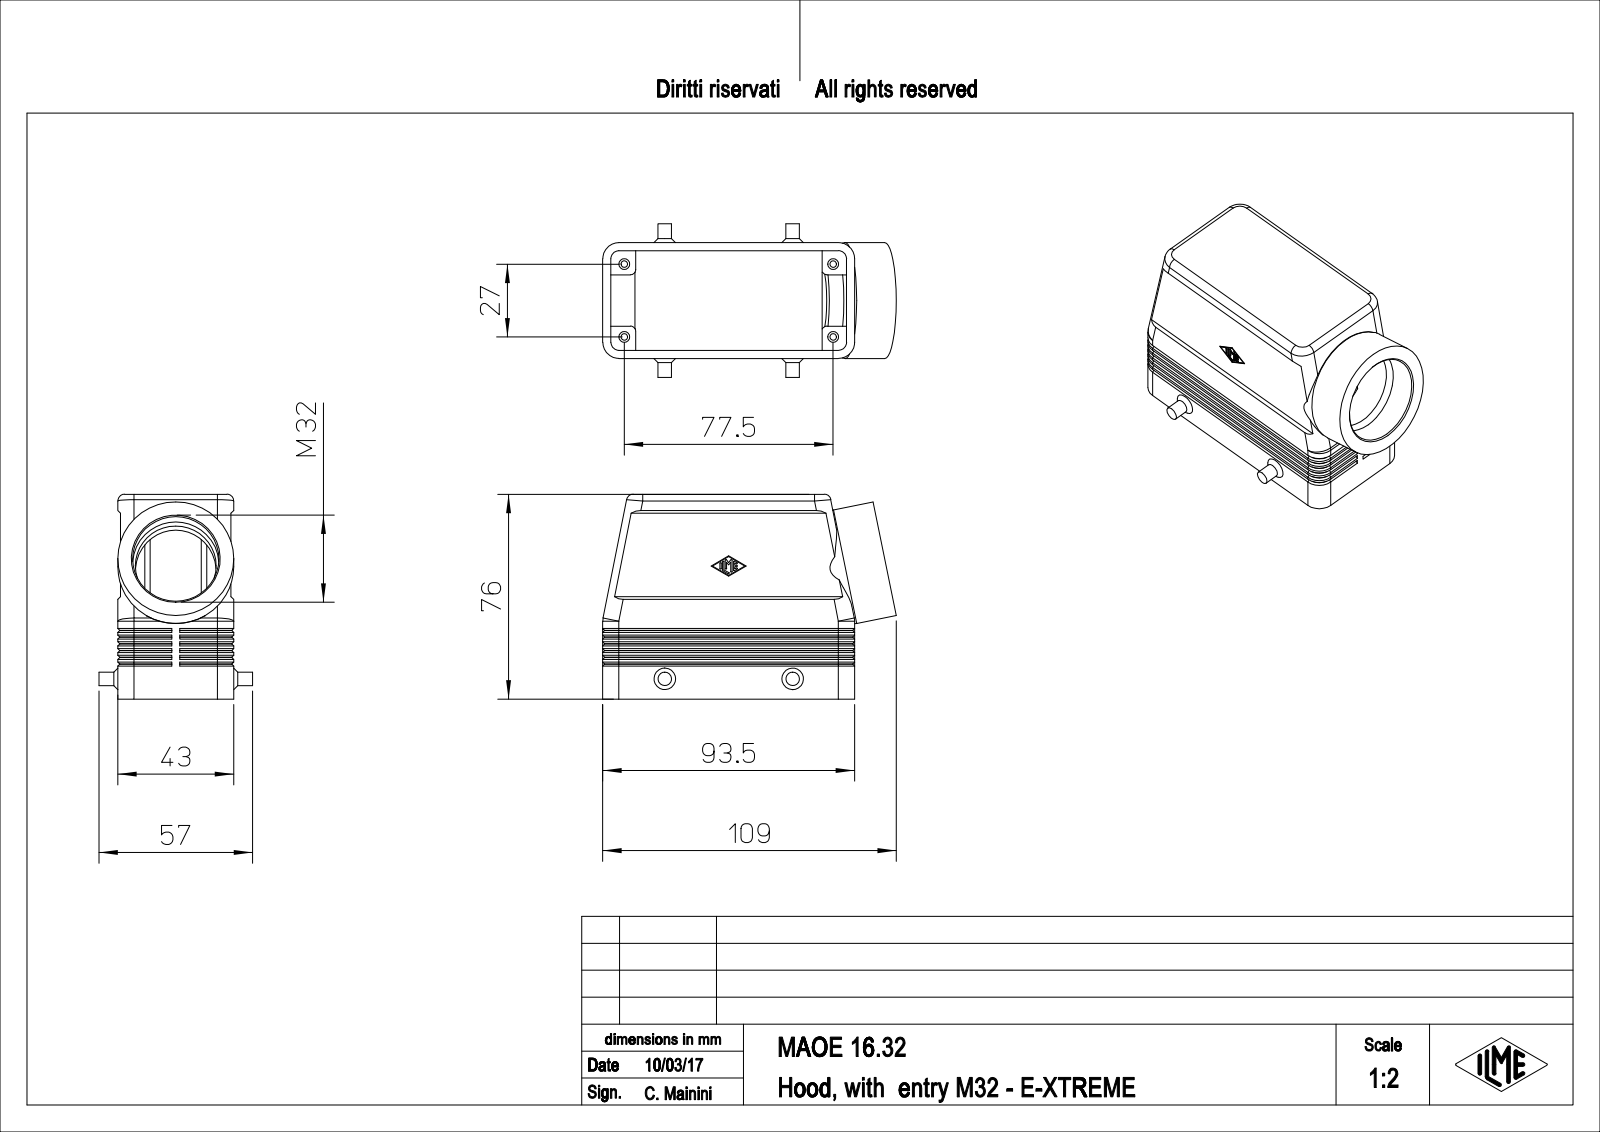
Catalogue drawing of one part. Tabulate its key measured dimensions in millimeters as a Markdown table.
| quantity | value |
| --- | --- |
| part name | MAOE_16.32 |
| STEP written by | PTC Creo Elements/Direct Modeling 19.0E 27-Jun-2016 (C) Parametric Technology GmbH (AUTOMOTIVE_DESIGN) |
| units | millimeters |
| bodies | 1 solid, 427 faces (228 planar, 119 cylindrical, 80 other) |
| overall size | 108.99 × 76 × 57 |
| volume | 79 913 mm³ |
| surface area | 47 427 mm² |
| round holes (diameter × count) | 2.46 × 4, 4 × 4, 30 × 1, 32 × 1 |
| round bosses / shafts (diameter × count) | 5 × 2, 43 × 1 |
| partial cylindrical surfaces (radius × count) | 0.25 × 14, 6 × 10, 2 × 4, 2.5 × 4, 3 × 4, 5.3 × 4 |
| main face-to-face distances | 3, 37, 2, 39, 1, 42, 40, 41, 43, 1.77 |
| hole center spacings | 27, 77.5, 82.07 |
